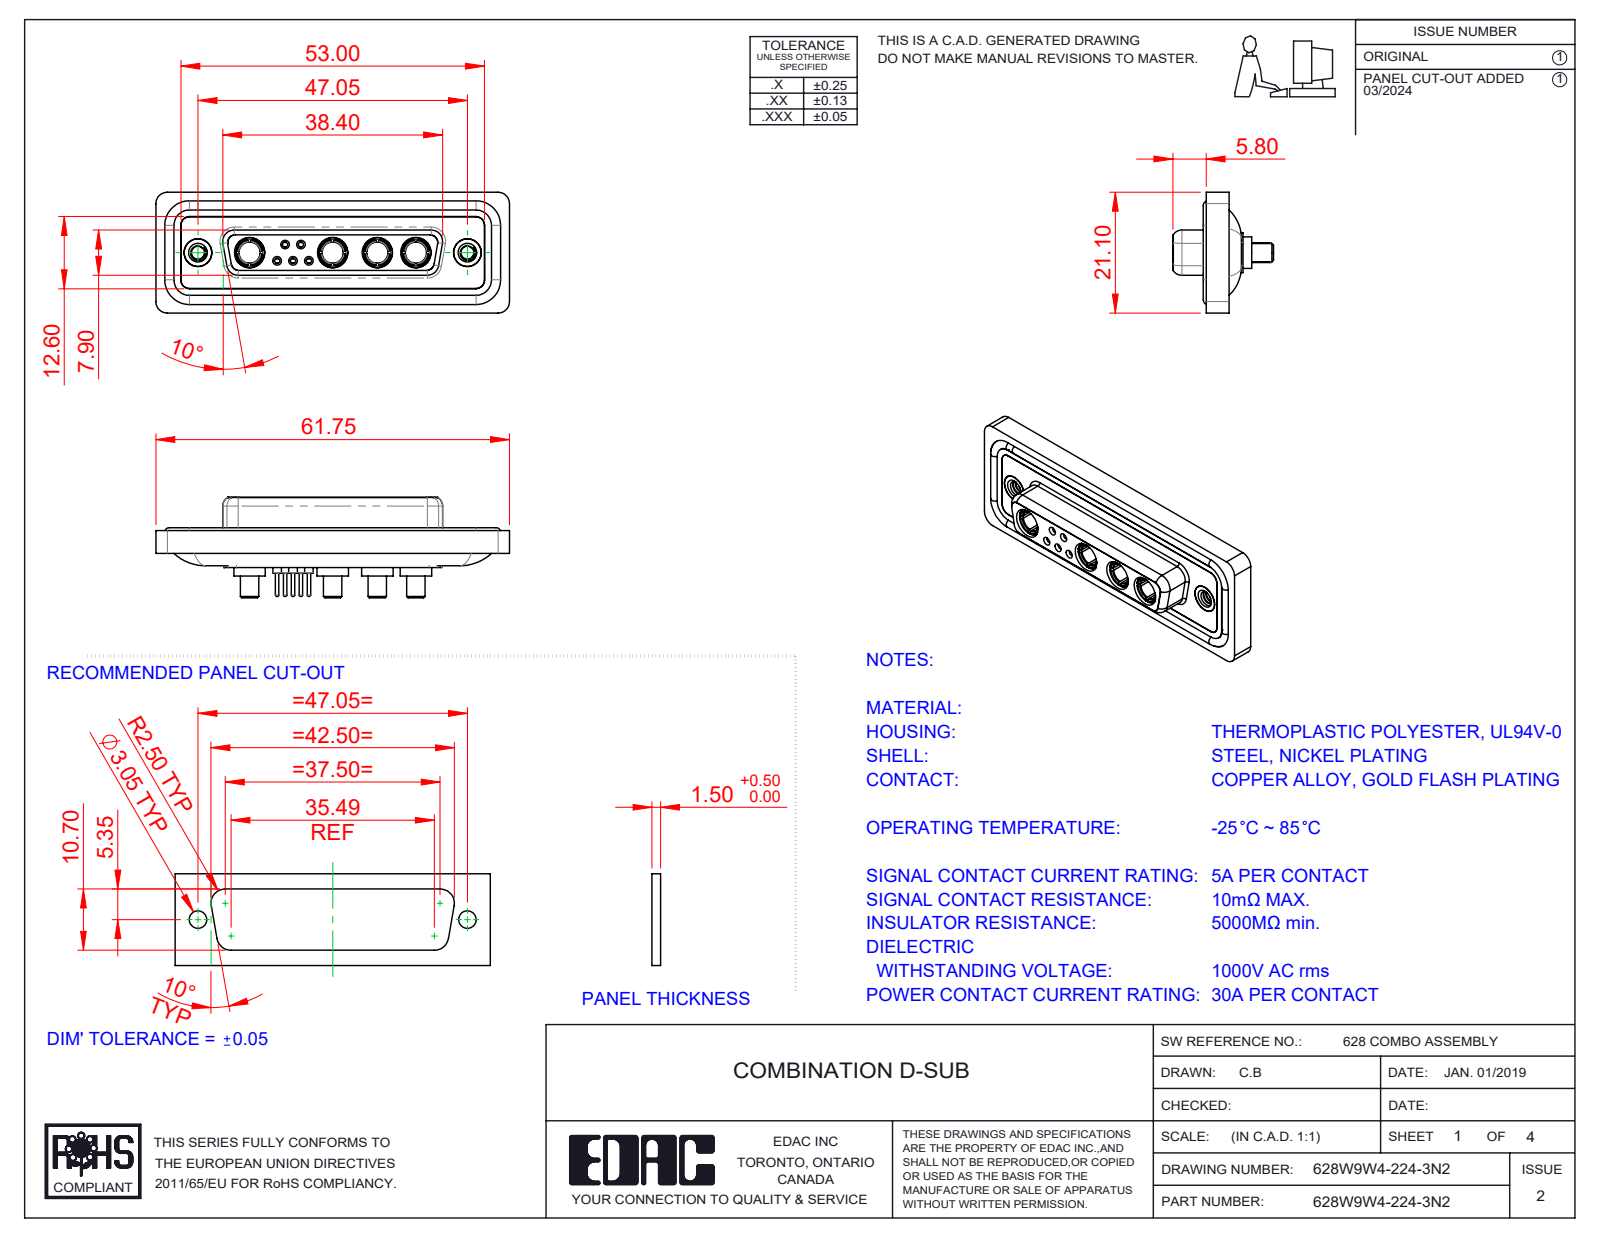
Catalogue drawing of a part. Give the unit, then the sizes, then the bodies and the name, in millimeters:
Units: millimetres
Overall size (bounding box): 61.75 × 21.1 × 17.55
Round holes (diameter × count): ⌀4.85 ×6, ⌀0.9 ×5, ⌀1.1 ×5, ⌀1.5 ×5, ⌀2 ×5, ⌀3.7 ×4, ⌀5.3 ×4, ⌀1.6 ×3, ⌀1.7 ×2, ⌀2.26 ×2, ⌀4 ×2, ⌀4.05 ×2
Round bosses / shafts (diameter × count): ⌀1.6 ×6, ⌀2.2 ×5, ⌀0.6 ×5, ⌀5.5 ×4, ⌀5.2 ×4, ⌀4.96 ×4, ⌀4.75 ×4, ⌀3.75 ×4
Partial cylindrical surfaces — rounded edges, fillets, slot ends (radius × count): R1.5 ×22, R2 ×18, R1.35 ×8, R1.6 ×8, R0.25 ×4, R0.5 ×4, R0.6 ×4, R0.65 ×4
Main face-to-face distances: 0.4, 1.8, 7.45, 5.65, 0.5, 7.05, 6.6, 1.6, 1.1, 2.9
Hole centre spacings: 3.16, 2.77, 5.03, 2.76, 4.4, 5.02, 5.54, 5.73
Volume: 8 252 mm³ · Surface area: 13 580 mm²
Bodies: 20 solids, 957 faces (296 planar, 375 cylindrical, 286 other)
Part name (STEP PRODUCT): 628Combo Shell Front_25 Contacts; 628Combo Contact Row 1_24; 628Combo Waterproof Housing_25 Contacts; Power Socket_30A S (+5 more)
STEP written by: SolidWorks 2023 (CONFIG_CONTROL_DESIGN)
